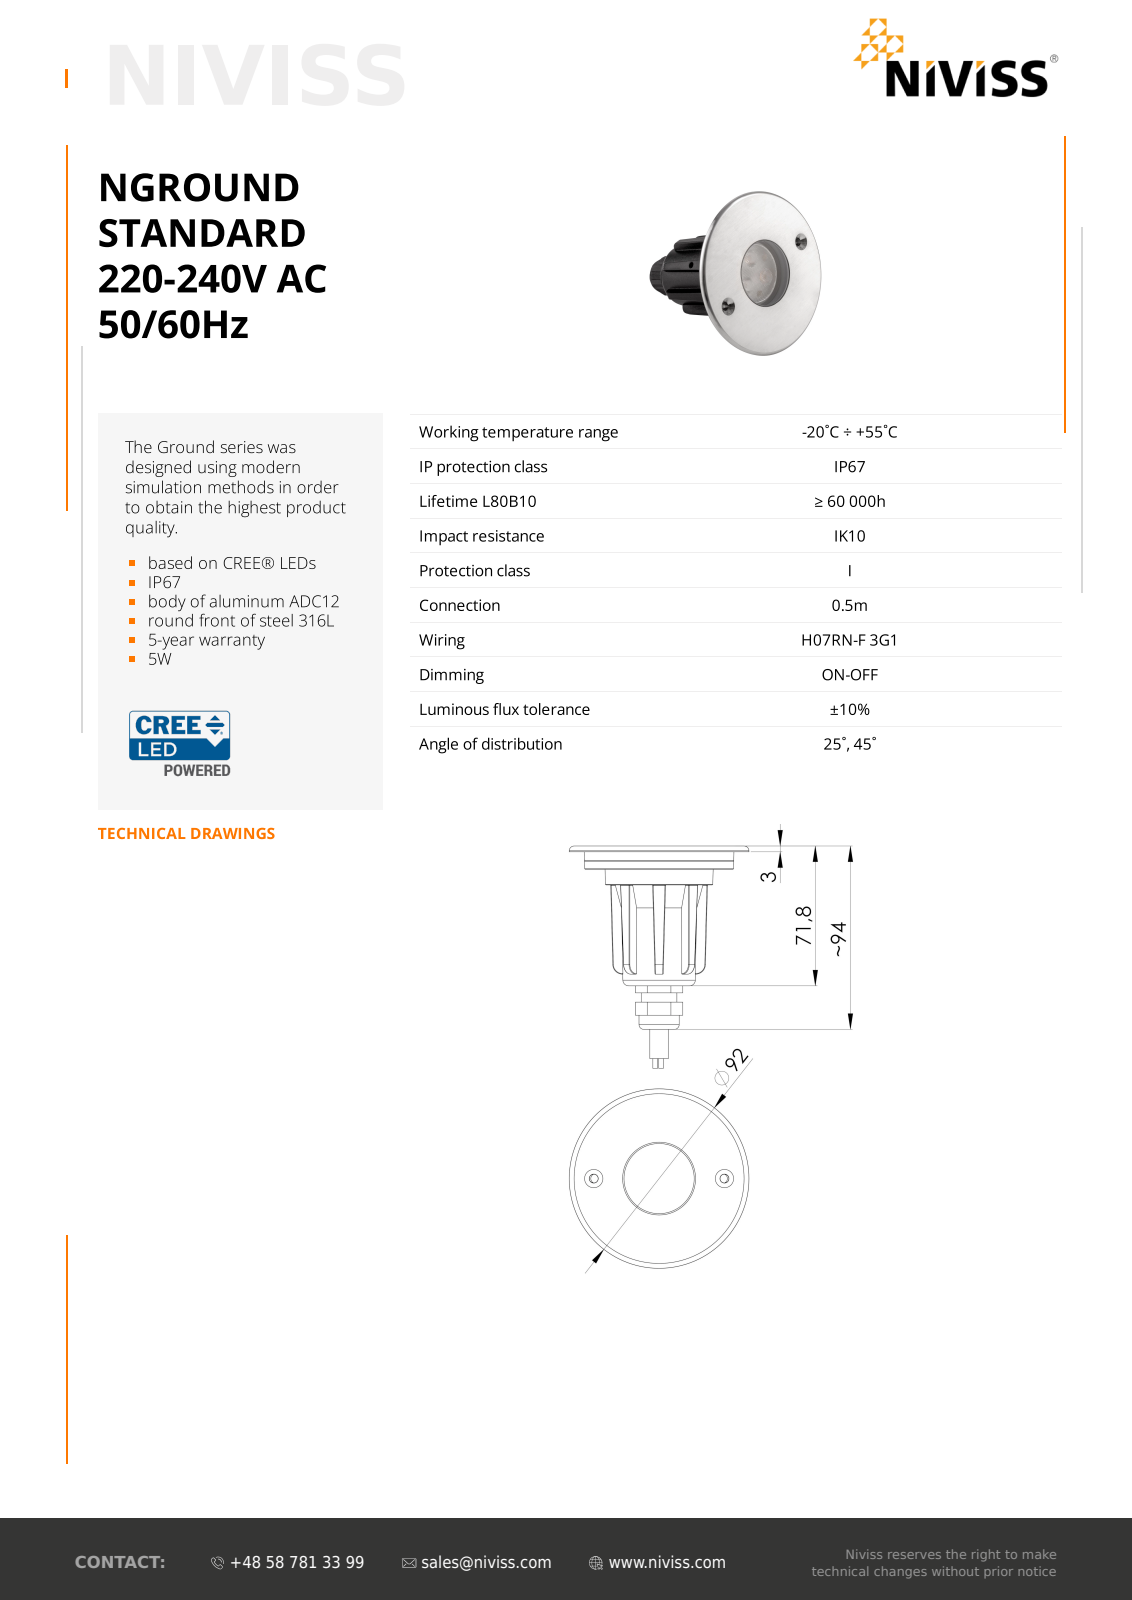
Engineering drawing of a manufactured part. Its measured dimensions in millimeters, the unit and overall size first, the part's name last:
Units: millimetres
Overall size (bounding box): 152.72 × 92.16 × 92.16
Round holes (diameter × count): ⌀3.3 ×5, ⌀4.1 ×4, ⌀9.5 ×4, ⌀2.05 ×3, ⌀2.5 ×2, ⌀2.7 ×2, ⌀2.9 ×2, ⌀4.5 ×2, ⌀0.3 ×1, ⌀8.3 ×1, ⌀14 ×1, ⌀14.5 ×1
Round bosses / shafts (diameter × count): ⌀4 ×8, ⌀9.3 ×4, ⌀4.9 ×4, ⌀2.5 ×4, ⌀6 ×2, ⌀1 ×2, ⌀46 ×1, ⌀37 ×1
Partial cylindrical surfaces — rounded edges, fillets, slot ends (radius × count): R0.3 ×44, R0.7 ×16, R5 ×8, R0.8 ×4, R1.5 ×4, R1.25 ×3, R1.03 ×2, R2.5 ×2
Main face-to-face distances: 7.5, 4.5, 9, 3, 12, 7.3, 7, 1.7, 0.7, 8
Hole centre spacings: 32.5, 45.96, 65, 17.25, 18.42, 35.9, 45.84, 46.08
Volume: 112 696 mm³ · Surface area: 62 904 mm²
Bodies: 25 solids, 1939 faces (942 planar, 322 cylindrical, 675 other)
Part name (STEP PRODUCT): DK140202DD08_6; PRZEWOD 2_9; screwM4x6_5; gla-35_asm_6 (+8 more)
STEP written by: SolidWorks 2017 (CONFIG_CONTROL_DESIGN)
